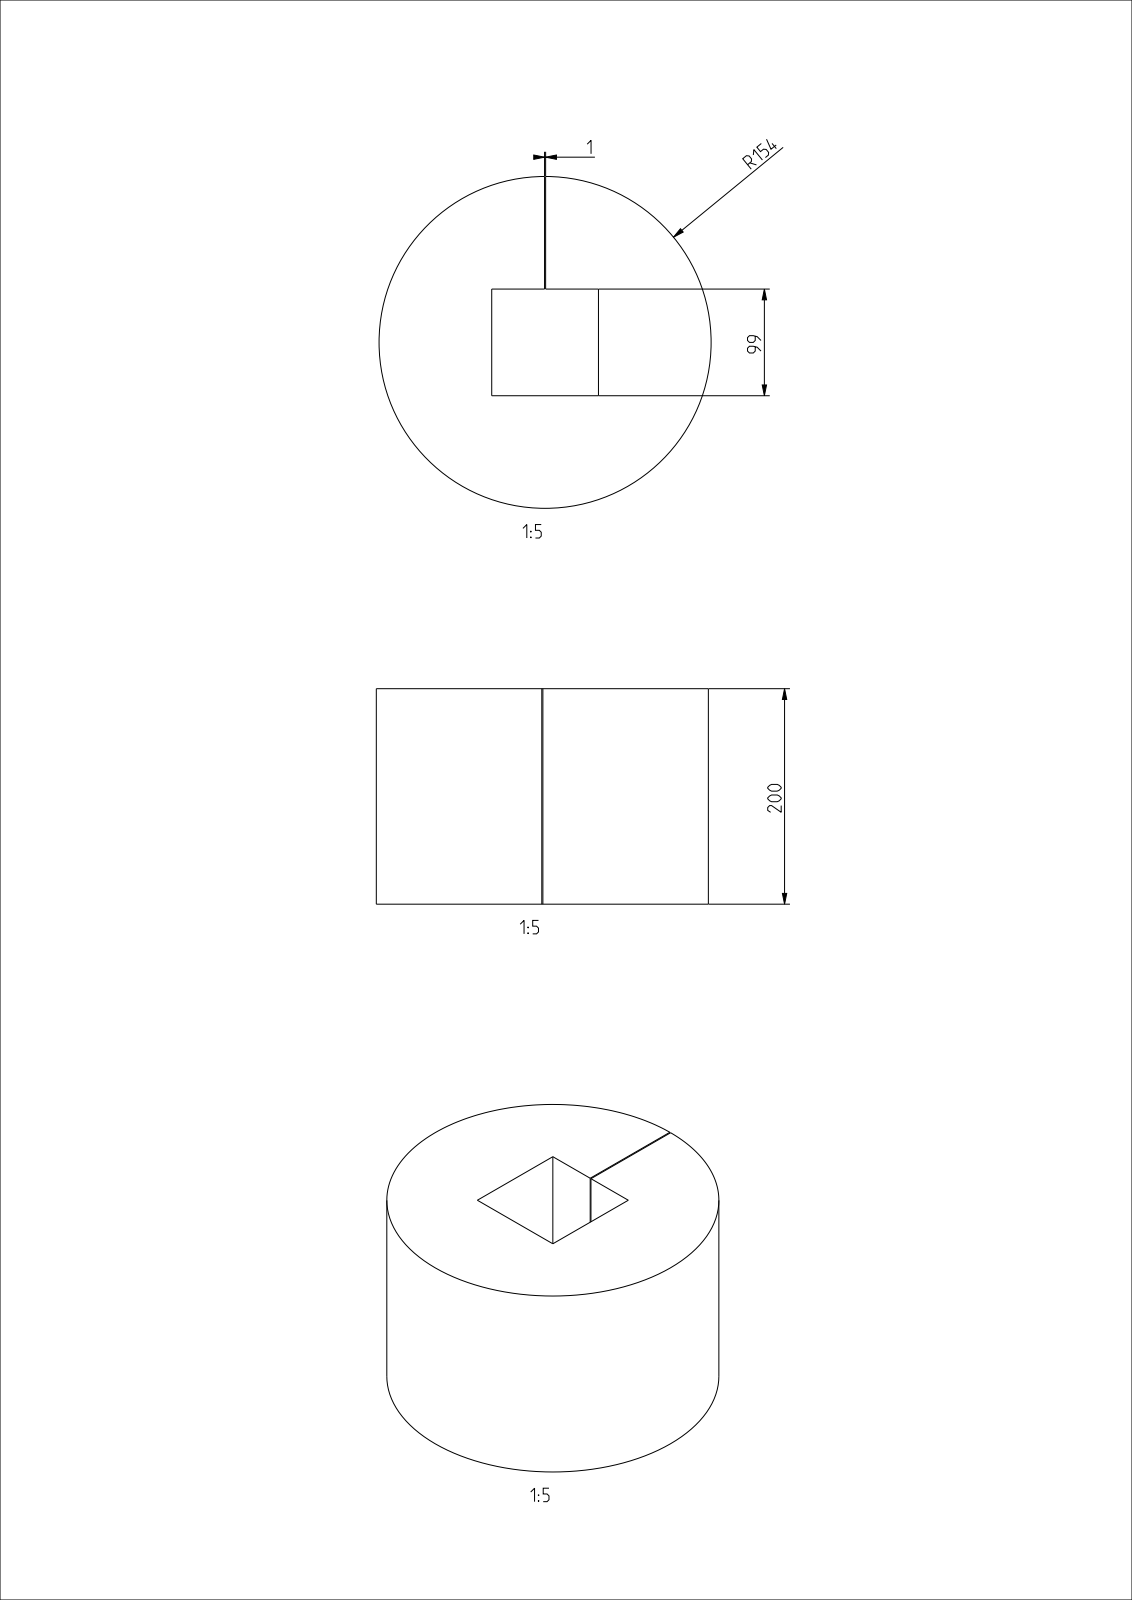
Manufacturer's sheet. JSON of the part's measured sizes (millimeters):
{"part_name": "47673-M", "step_written_by": "CREO PARAMETRIC BY PTC INC, 2022281 (AUTOMOTIVE_DESIGN)", "units": "millimeters", "bodies": {"solids": 1, "faces": 10, "planar": 9, "cylindrical": 1, "other": 0}, "overall_size": [308, 308, 200], "volume_mm3": 12920000, "surface_area_mm2": 443323, "round_bosses_or_shafts": [[308, 1]], "face_to_face_distances": [200, 49, 50, 99, 1]}
